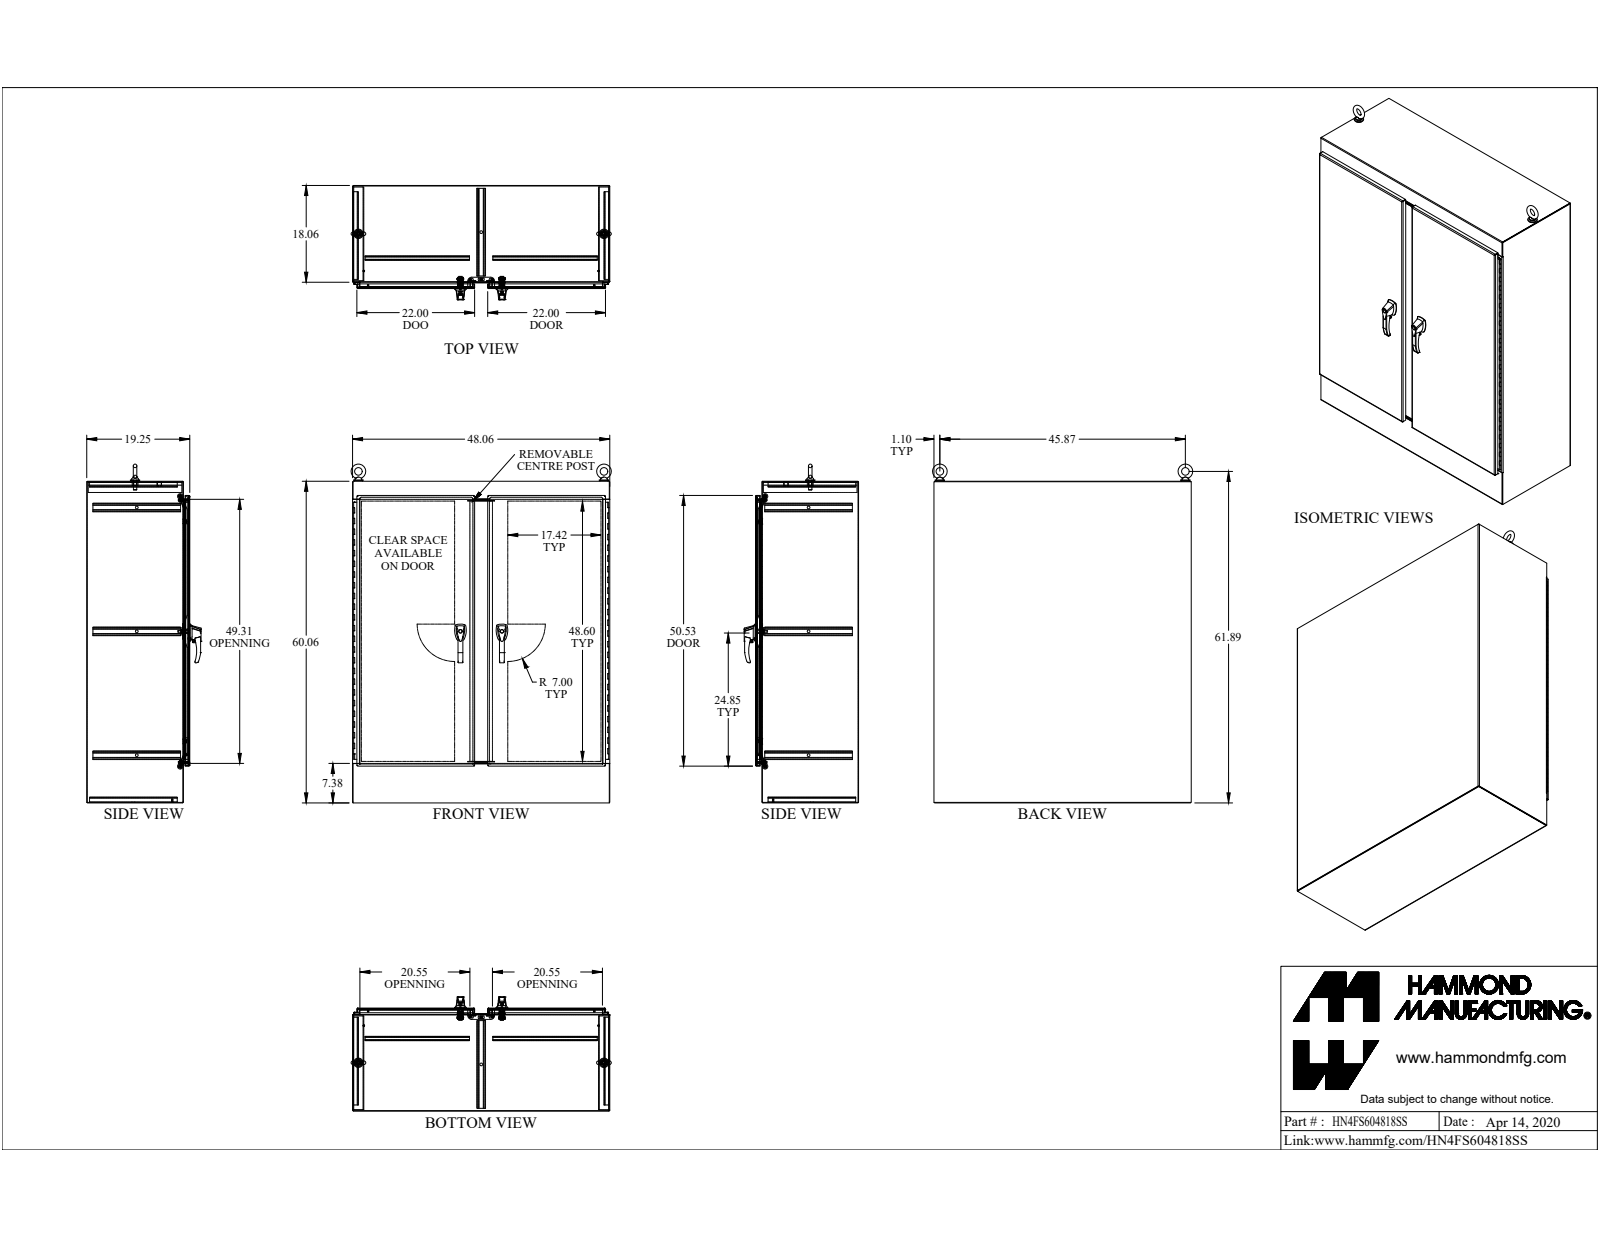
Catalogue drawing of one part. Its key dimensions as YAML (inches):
part_name: "HN4FS604818SS"
step_written_by: "SolidWorks 2019 (CONFIG_CONTROL_DESIGN)"
units: inches
bodies: {solids: 108, faces: 3018, planar: 1568, cylindrical: 1082, other: 368}
overall_size: [63.256, 48.604, 21.362]
volume: 1168
surface_area: 24575
round_holes:
  - {diameter: 0.304, count: 16}
  - {diameter: 0.35, count: 8}
  - {diameter: 0.25, count: 5}
  - {diameter: 0.201, count: 4}
  - {diameter: 0.281, count: 4}
  - {diameter: 0.313, count: 4}
  - {diameter: 0.39, count: 4}
  - {diameter: 0.5, count: 4}
  - {diameter: 0.313, count: 3}
  - {diameter: 0.11, count: 2}
  - {diameter: 0.173, count: 2}
  - {diameter: 0.233, count: 2}
round_bosses_or_shafts:
  - {diameter: 0.75, count: 4}
  - {diameter: 0.625, count: 4}
  - {diameter: 0.44, count: 4}
  - {diameter: 0.37, count: 4}
  - {diameter: 0.313, count: 4}
  - {diameter: 0.25, count: 4}
  - {diameter: 0.293, count: 3}
  - {diameter: 0.246, count: 3}
partial_cylinders:
  - {radius: 0.043, count: 54}
  - {radius: 0.138, count: 48}
  - {radius: 0.5, count: 33}
  - {radius: 0.018, count: 32}
  - {radius: 0.06, count: 24}
  - {radius: 0.125, count: 23}
  - {radius: 0.1, count: 22}
  - {radius: 0.318, count: 16}
face_to_face_distances: [0.095, 19.152, 19.057, 19.247, 47.965, 59.965, 1.187, 17.965, 47.87, 48.06]
hole_center_spacings: [6, 46.715, 12, 47.857, 18, 49.702, 24, 46.328]
